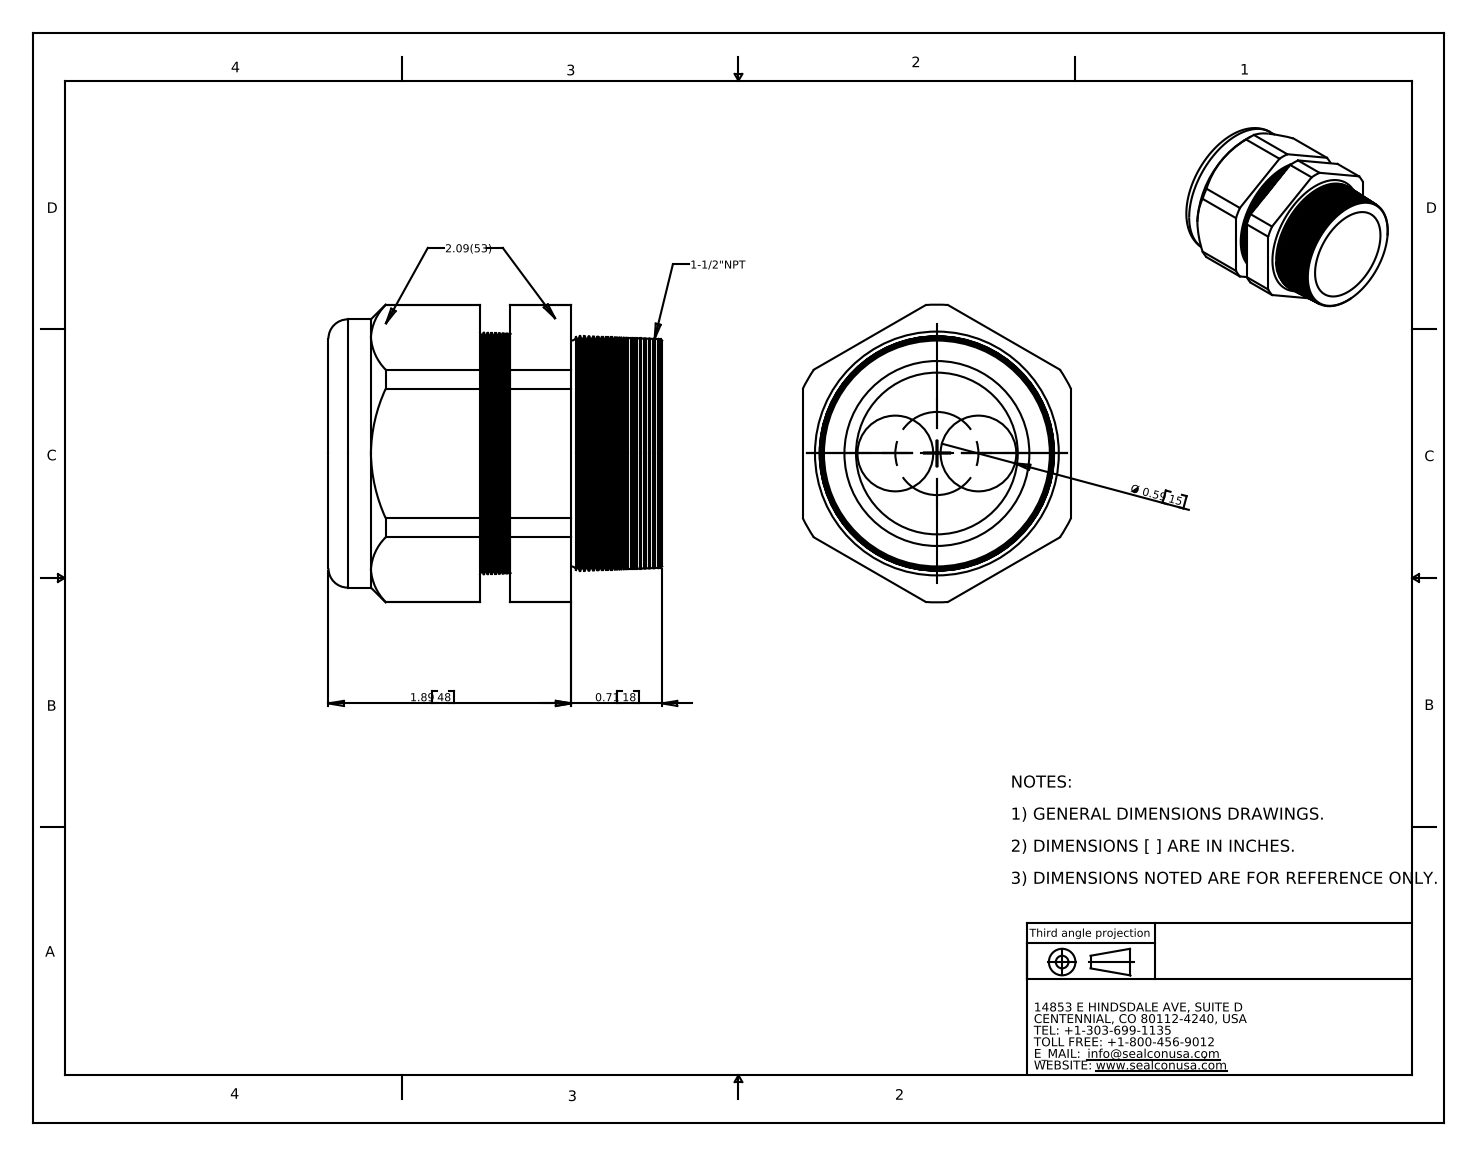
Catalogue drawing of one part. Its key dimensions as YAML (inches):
part_name: "CD36N4-GY"
step_written_by: "SolidWorks 2007 (CONFIG_CONTROL_DESIGN)"
units: inches
bodies: {solids: 2, faces: 239, planar: 21, cylindrical: 24, other: 194}
overall_size: [2.68, 2.32, 2.09]
volume: 5.403
surface_area: 43.3
round_holes:
  - {diameter: 0.59, count: 2}
  - {diameter: 1.24, count: 1}
  - {diameter: 1.26, count: 1}
round_bosses_or_shafts:
  - {diameter: 2.09, count: 1}
partial_cylinders:
  - {radius: 1.16, count: 1}
face_to_face_distances: [2.09, 1.418, 1.181, 0.237, 1.89, 0.709, 0.472, 2.68, 1.499, 1.262]
hole_center_spacings: [0.324, 0.648]
